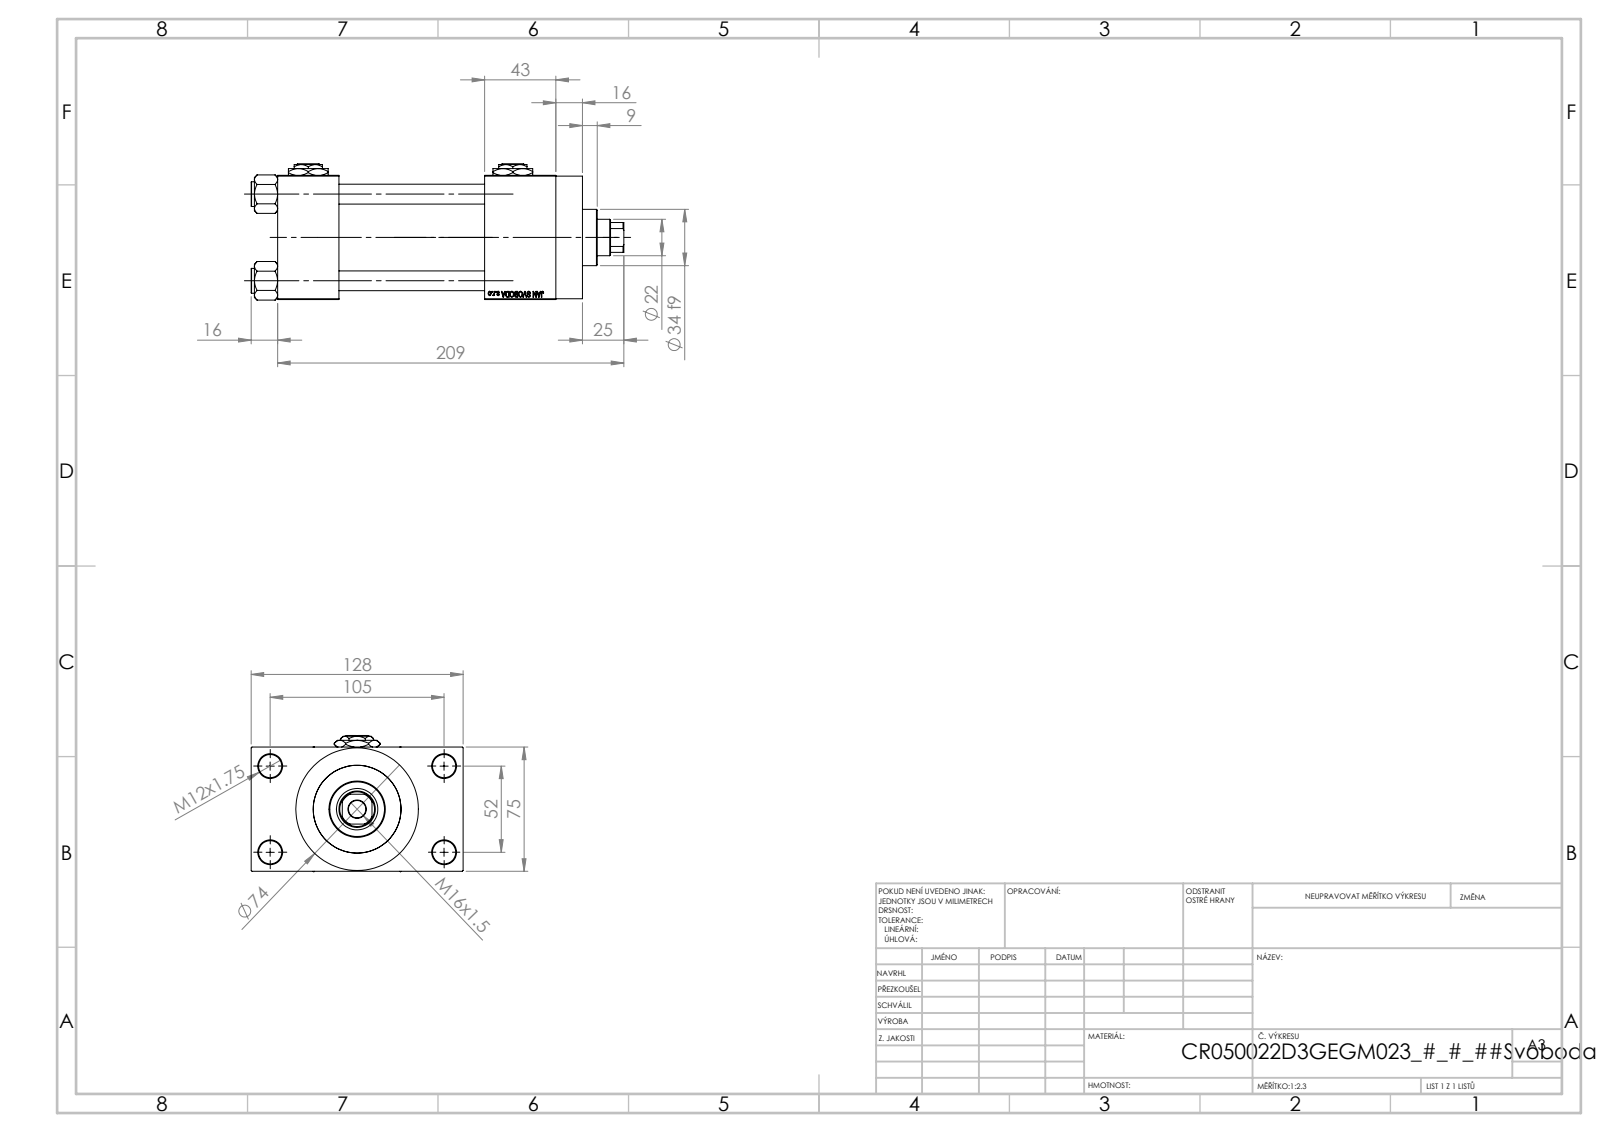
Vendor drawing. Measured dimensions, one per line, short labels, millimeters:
name: V215CR_D_TYCINKA; V215CR_VCP_D; NUT_M5_D; V215CR_D_Body (+2 more)
written by: SolidWorks 2019 (CONFIG_CONTROL_DESIGN)
unit: mm
bodies: 13 solids, 1205 faces (545 planar, 100 cylindrical, 560 other)
size: 225 × 128 × 82.27
volume: 842 138 mm³; area: 185 771 mm²
holes: 4× ⌀12, 4× ⌀14, 2× ⌀7, 2× ⌀20.96, 2× ⌀30, 1× ⌀10.5, 1× ⌀22, 1× ⌀25, 1× ⌀41, 1× ⌀50, 1× ⌀53
bosses: 4× ⌀15, 1× ⌀74, 1× ⌀56, 1× ⌀34
rounds: 1× R10.5
face distances: 75, 88, 37, 125, 26.5, 101.5, 168, 131, 43, 16
hole spacings: 26.35, 36.98, 52.3, 58.43, 58.59, 78.65, 94.37, 52
